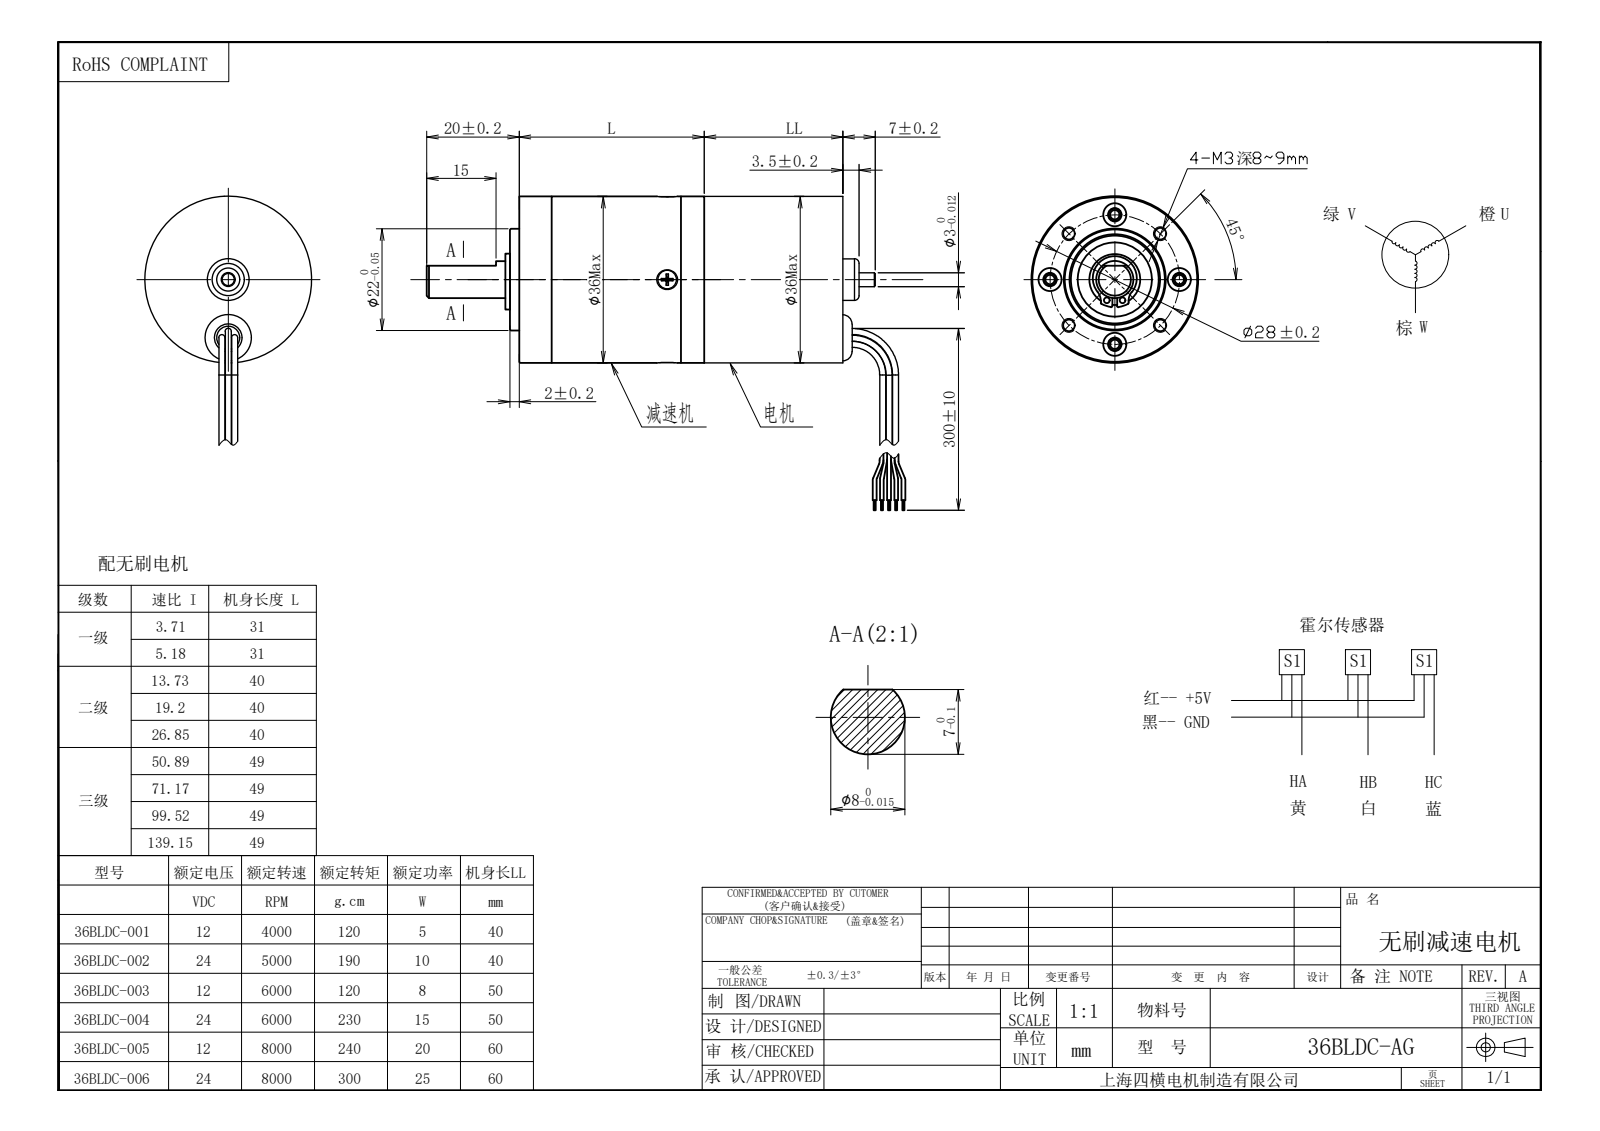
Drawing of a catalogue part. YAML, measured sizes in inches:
part_name: "Цб3; deep groove ball bearings gb_Rolling bearings 619-8 GB 276-94; PLA36-003前端盖; 无刷电机 (+8 more)"
step_written_by: "SolidWorks 2020 (AUTOMOTIVE_DESIGN)"
units: inches
bodies: {solids: 22, faces: 1566, planar: 165, cylindrical: 739, other: 662}
overall_size: [3.308, 1.943, 1.417]
volume: 2.831
surface_area: 36.54
round_holes:
  - {diameter: 0.081, count: 4}
  - {diameter: 0.098, count: 4}
  - {diameter: 0.114, count: 4}
  - {diameter: 0.205, count: 4}
  - {diameter: 0.118, count: 3}
  - {diameter: 0.094, count: 2}
  - {diameter: 0.197, count: 2}
  - {diameter: 0.291, count: 1}
  - {diameter: 0.315, count: 1}
  - {diameter: 0.492, count: 1}
  - {diameter: 0.604, count: 1}
  - {diameter: 0.669, count: 1}
round_bosses_or_shafts:
  - {diameter: 0.051, count: 10}
  - {diameter: 0.177, count: 4}
  - {diameter: 0.098, count: 4}
  - {diameter: 0.157, count: 2}
  - {diameter: 0.079, count: 2}
  - {diameter: 1.417, count: 1}
  - {diameter: 0.866, count: 1}
  - {diameter: 0.862, count: 1}
partial_cylinders:
  - {radius: 0.008, count: 92}
  - {radius: 0.11, count: 92}
  - {radius: 0.063, count: 4}
  - {radius: 0.024, count: 2}
  - {radius: 0.431, count: 1}
  - {radius: 0.476, count: 1}
face_to_face_distances: [0.197, 1.024, 0.866, 0.669, 0.827, 1.693, 0.079, 1.22, 0.445, 0.579]
hole_center_spacings: [0.422, 0.551, 0.78, 1.019, 1.102, 0.309, 0.323, 0.398]
